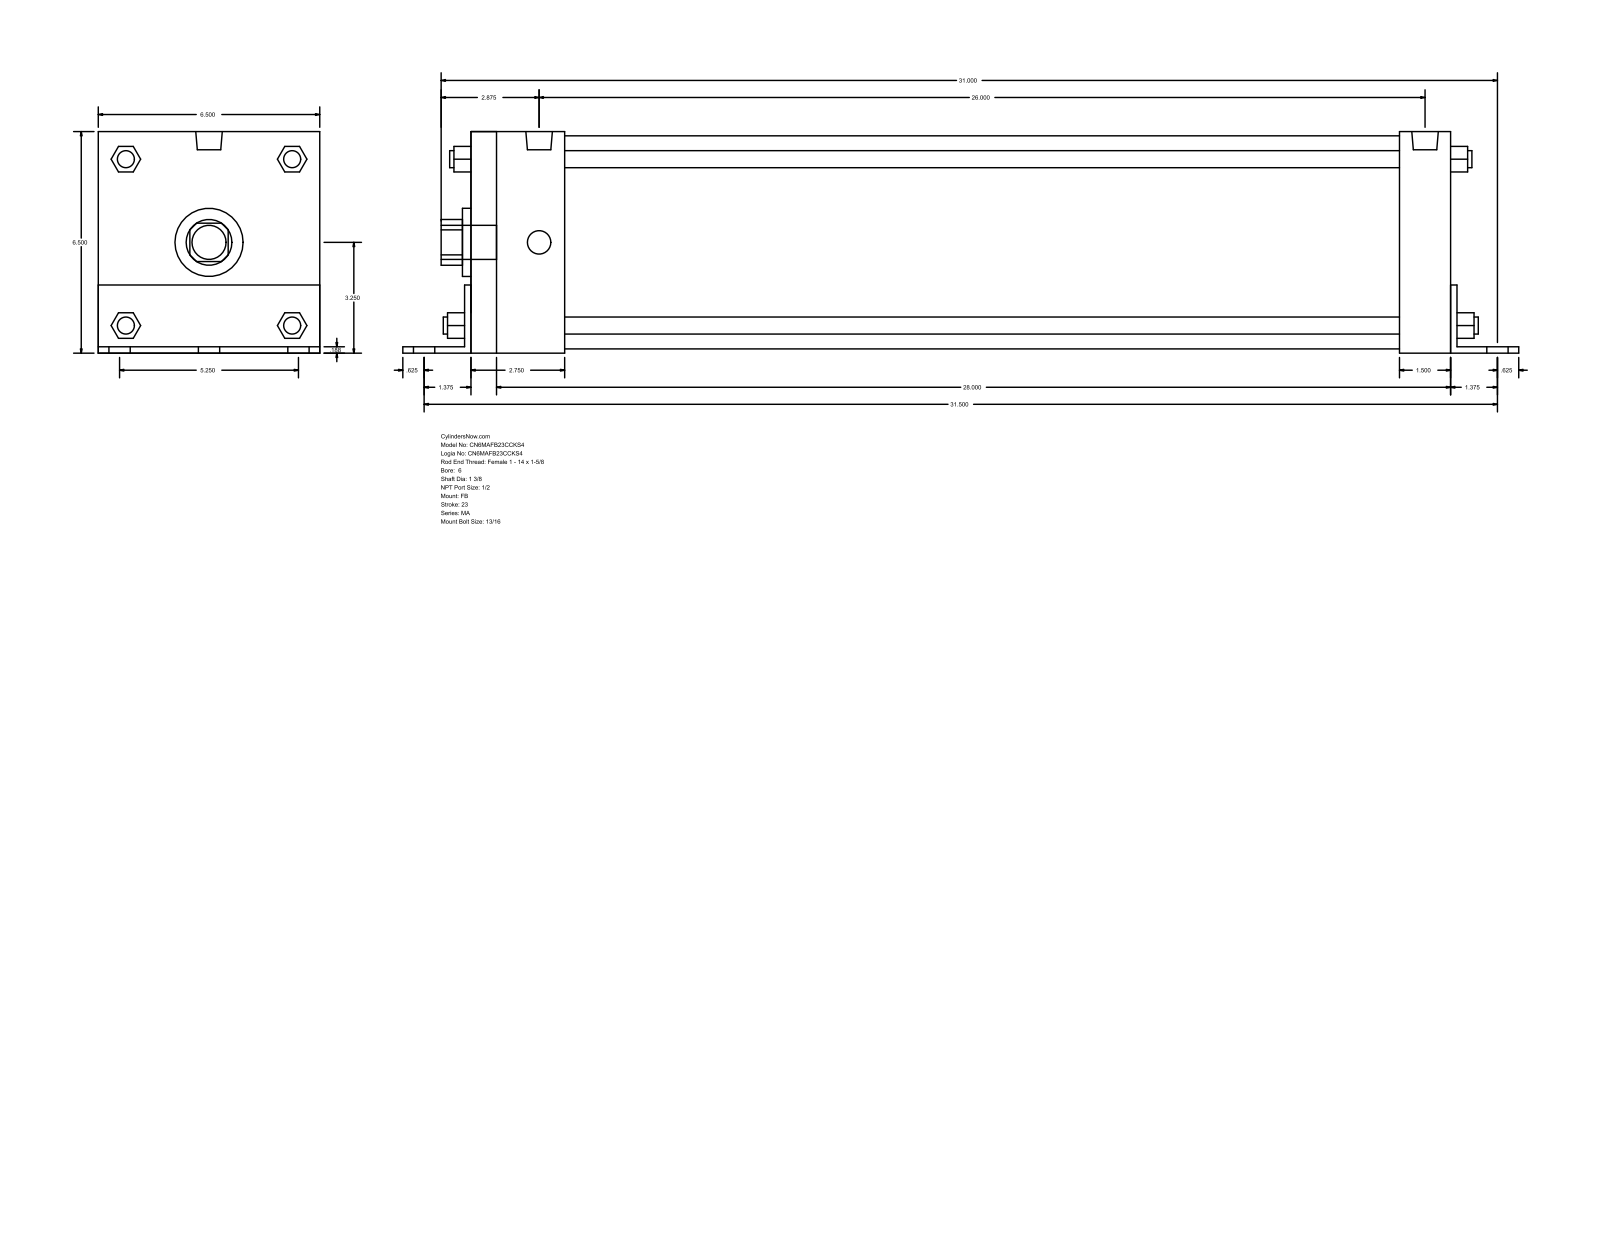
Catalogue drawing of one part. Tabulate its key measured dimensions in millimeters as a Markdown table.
| quantity | value |
| --- | --- |
| part name | MA_FB__0600_1.375 |
| STEP written by | GSSL Pune (CONFIG_CONTROL_DESIGN) |
| units | millimeters |
| bodies | 0 solids, 140 faces (105 planar, 35 cylindrical, 0 other) |
| overall size | 828.67 × 165.15 × 165.1 |
| round holes (diameter × count) | 34.92 × 1, 50.8 × 1, 158.75 × 1 |
| round bosses / shafts (diameter × count) | 20.64 × 6, 17.46 × 4, 12.7 × 4, 19.77 × 2, 25.4 × 1 |
| partial cylindrical surfaces (radius × count) | 17.06 × 1, 32.05 × 1 |
| main face-to-face distances | 165.1, 4.76, 727.07, 165.15, 4.71, 160.39, 4.77, 38.1, 731.84, 736.6 |
